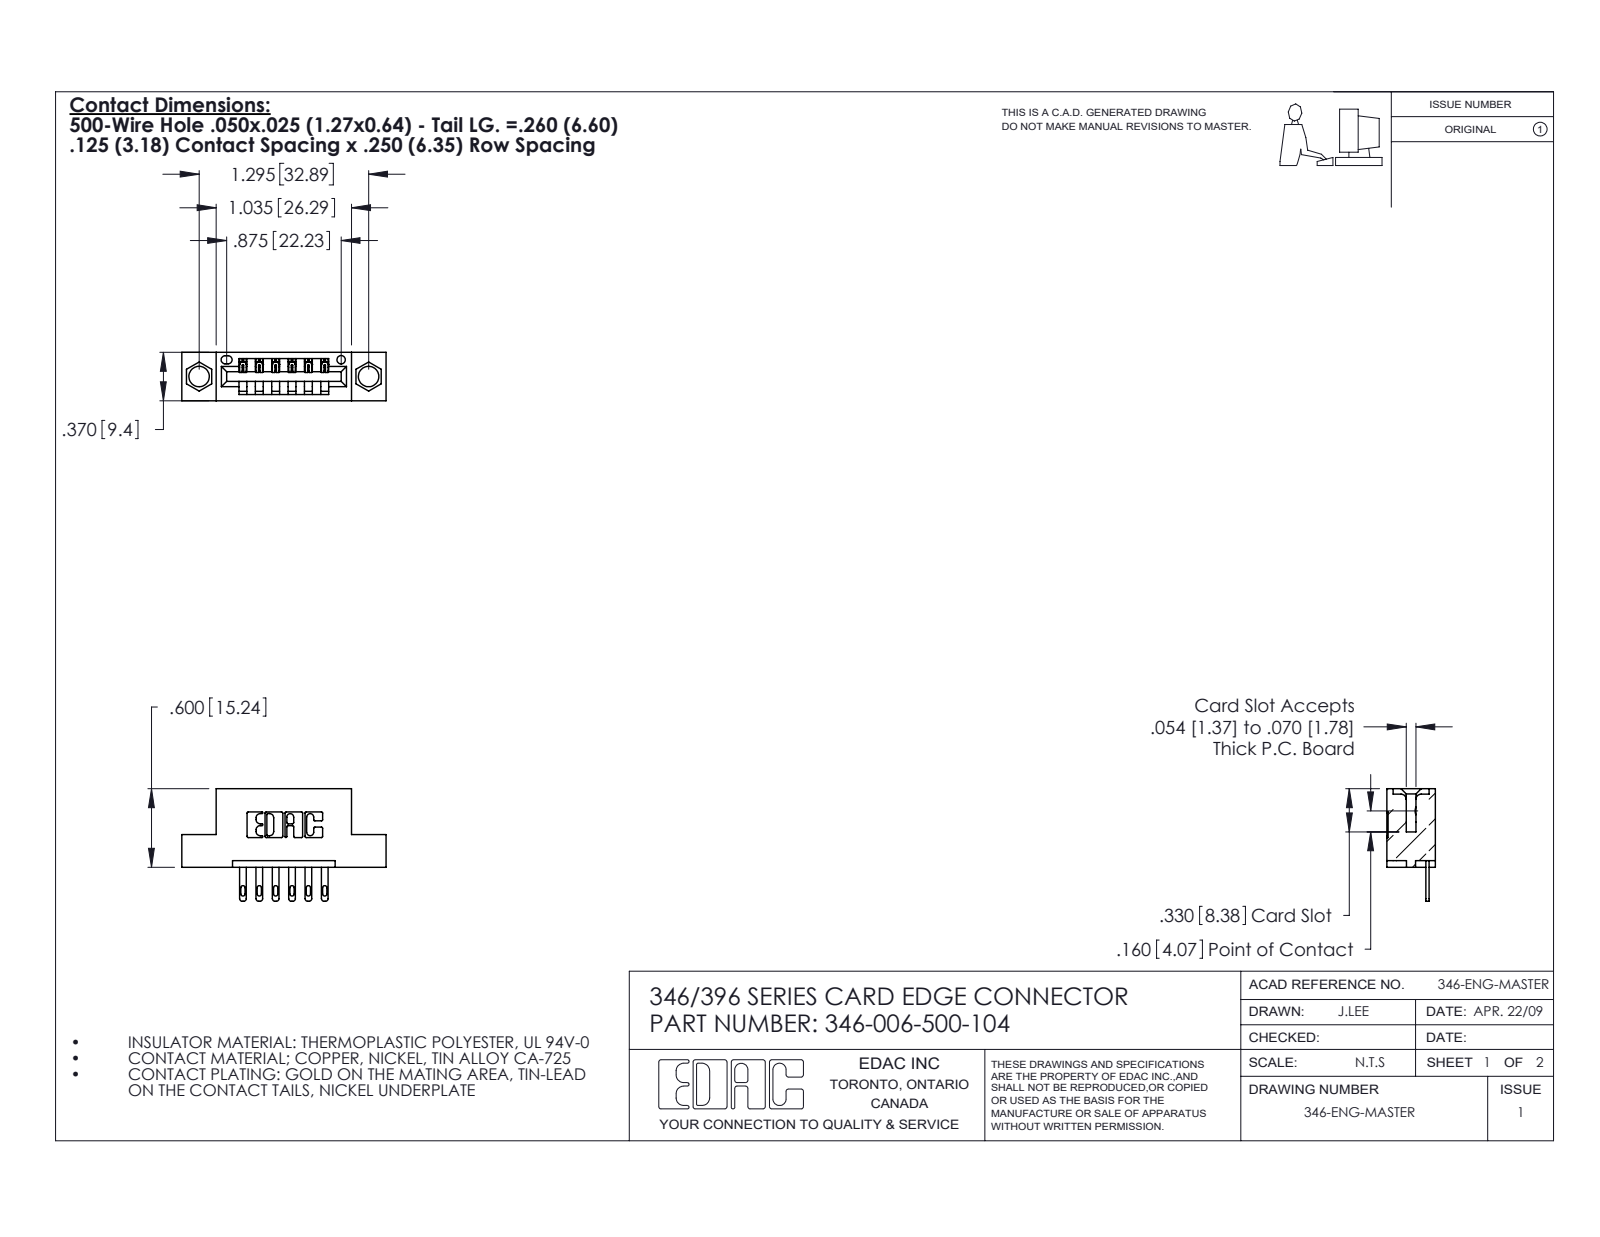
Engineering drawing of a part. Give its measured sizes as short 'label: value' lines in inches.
name: 346-006-500-104; 345-292-001_345-293-100; 346 Part_Flush Mounting Lugs - 0.156 Dia-TH
written by: SolidWorks 2020 (CONFIG_CONTROL_DESIGN)
unit: in
bodies: 7 solids, 460 faces (294 planar, 166 cylindrical, 0 other)
size: 1.56 × 0.86 × 0.37
volume: 0.21 in³; area: 5.837 in²
holes: 2× ⌀0.156, 1× ⌀0.064
rounds: 22× R0.01, 12× R0.006, 12× R0.016, 12× R0.02, 6× R0.007, 6× R0.031, 3× R0.026, 2× R0.031
face distances: 0.25, 0.37, 0.048, 0.322, 0.072, 0.298, 0.025, 0.148, 0.222, 0.1
hole spacings: 0.246, 1.092, 1.295
